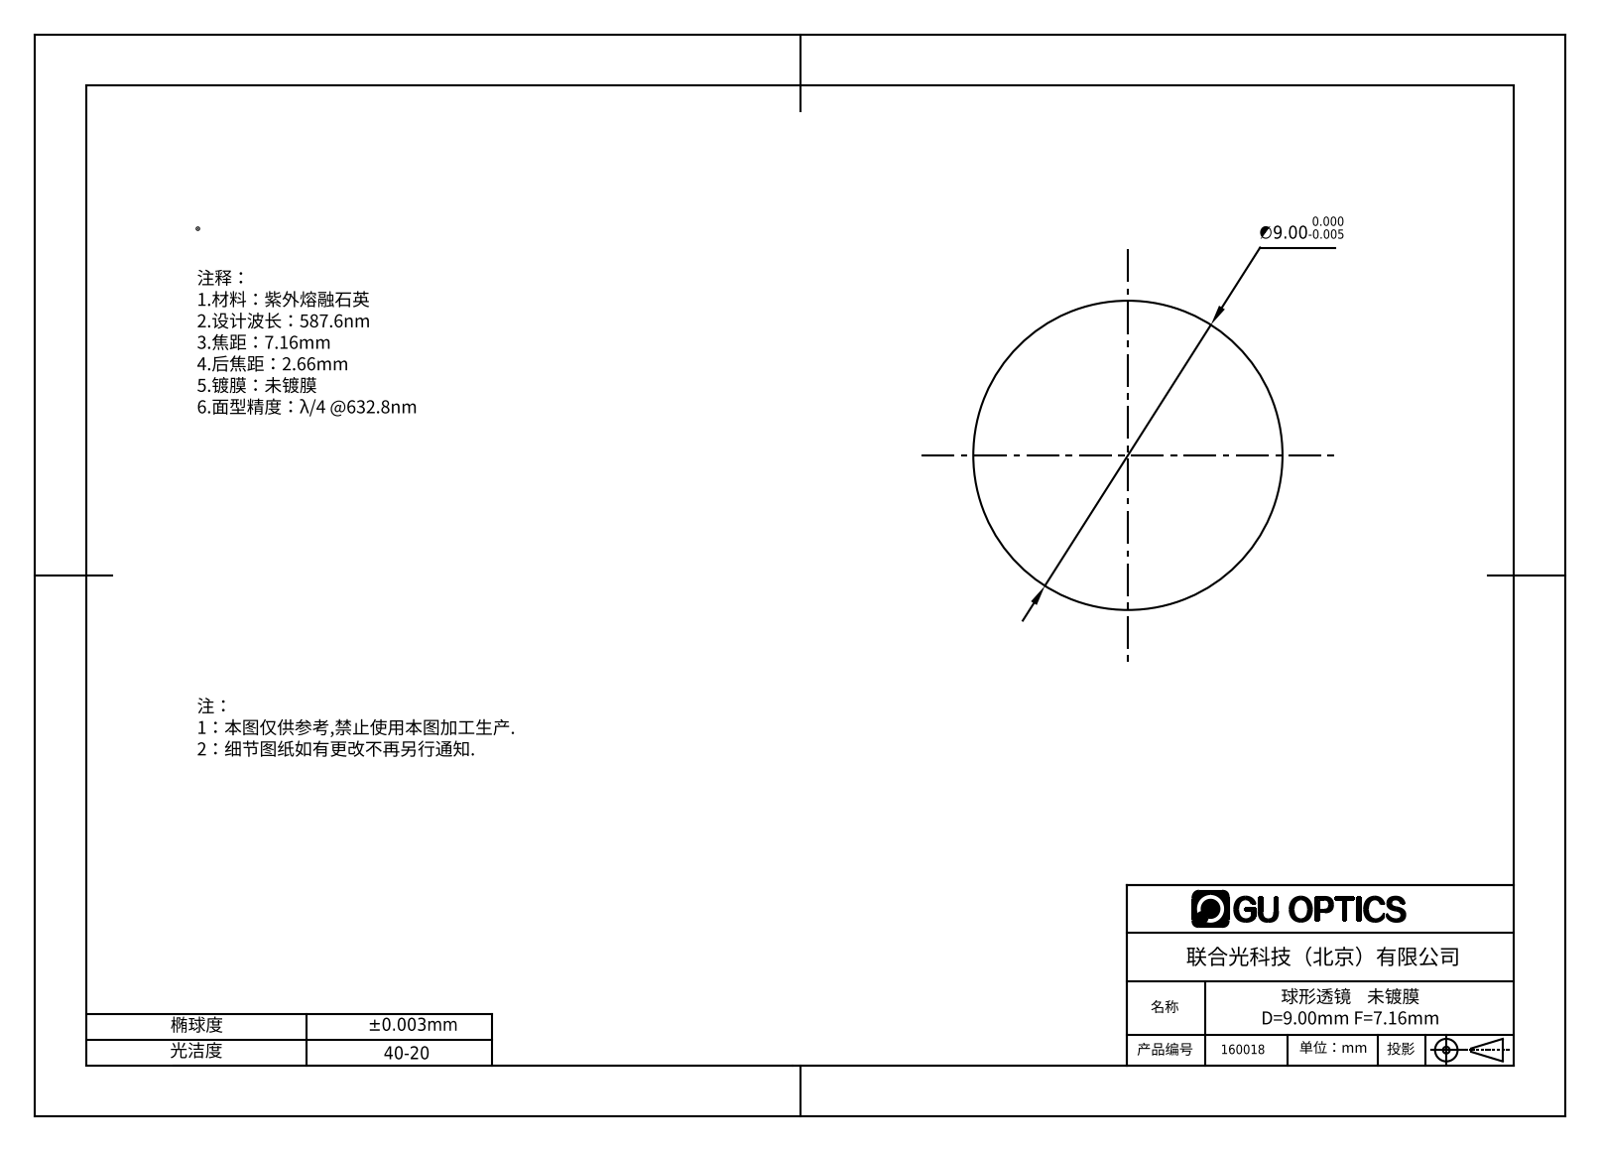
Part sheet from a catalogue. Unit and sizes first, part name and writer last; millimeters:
Units: millimetres
Overall size (bounding box): 9 × 9 × 9
Volume: 382 mm³ · Surface area: 254 mm²
Bodies: 1 solid, 2 faces (0 planar, 0 cylindrical, 2 other)
Part name (STEP PRODUCT): 160008
STEP written by: SolidWorks 2016 (CONFIG_CONTROL_DESIGN)
